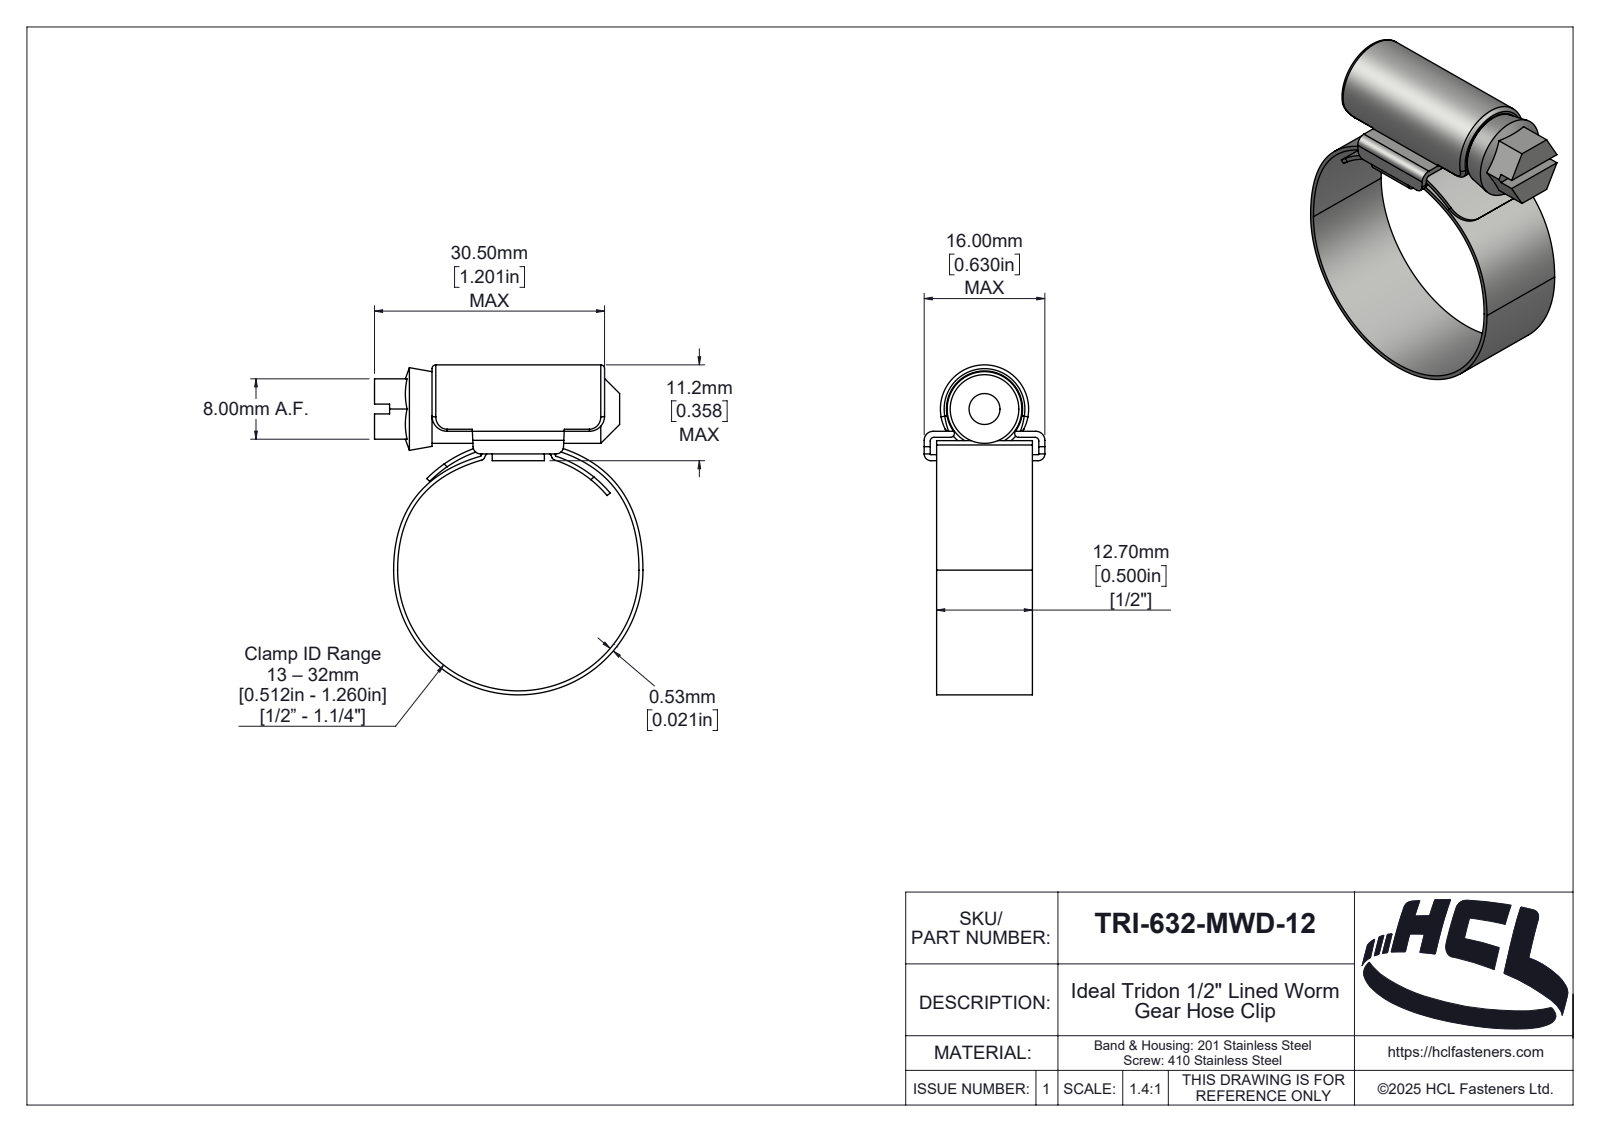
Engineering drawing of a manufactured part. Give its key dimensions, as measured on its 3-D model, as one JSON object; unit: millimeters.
{"part_name": "TRI-632-MWD-12", "step_written_by": "SolidWorks 2025 (AUTOMOTIVE_DESIGN)", "units": "millimeters", "bodies": {"solids": 3, "faces": 217, "planar": 49, "cylindrical": 99, "other": 69}, "overall_size": [43.73, 35.59, 16], "volume_mm3": 3536, "surface_area_mm2": 6180, "round_bosses_or_shafts": [[9.1, 1]], "partial_cylinders_radius": [[0.5, 10], [3, 4], [0.1, 2], [0.9, 2], [1, 2], [1.03, 2], [1.2, 2], [2, 2]], "face_to_face_distances": [0.8, 3.1, 2.3, 12.7, 3.9, 1.65, 14.35, 15.2, 0.85, 13.55]}
